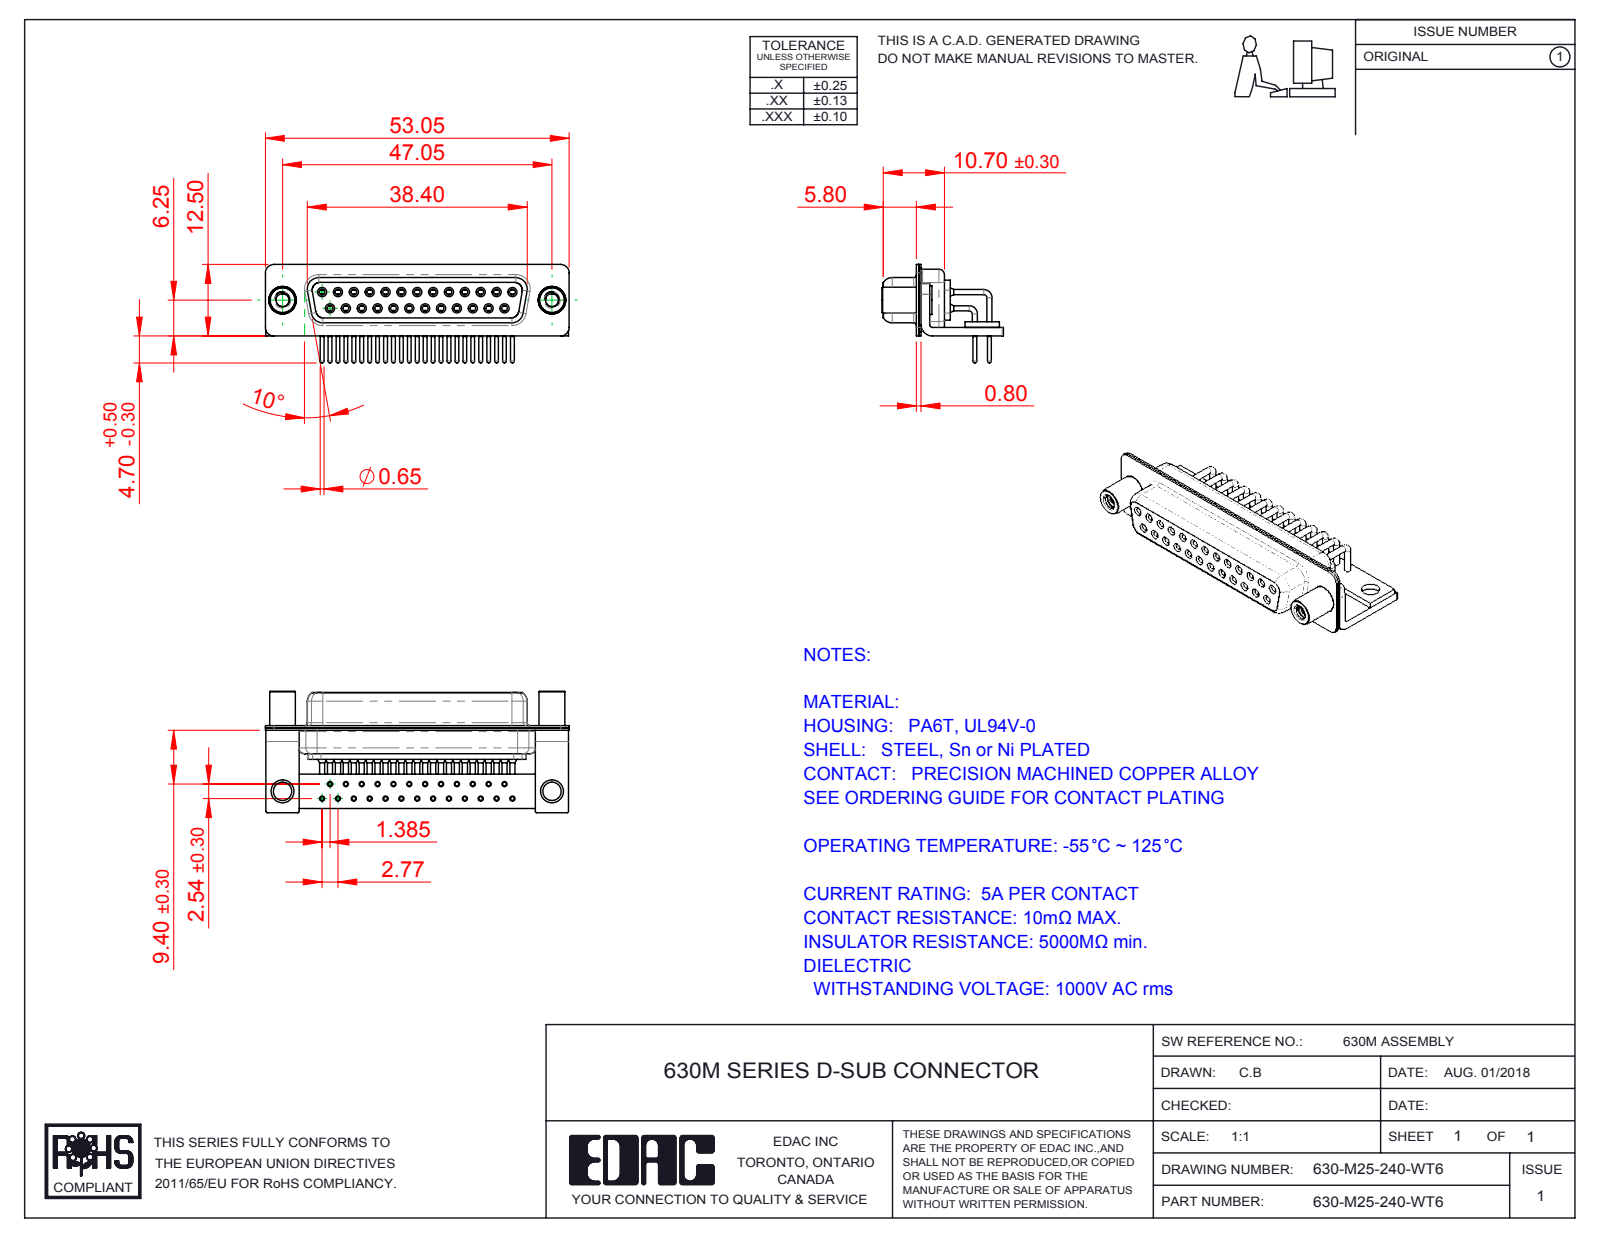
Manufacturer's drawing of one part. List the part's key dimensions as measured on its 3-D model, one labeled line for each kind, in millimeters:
Part name (STEP PRODUCT): 630-M25-240-WT6; 630M Housing_25 Contacts; 630M Shell Front_25 Contacts; 630M Shell Rear_25 Contacts (+5 more)
STEP written by: SolidWorks 2016 (CONFIG_CONTROL_DESIGN)
Units: millimetres
Bodies: 33 solids, 1754 faces (470 planar, 826 cylindrical, 458 other)
Overall size (bounding box): 53.05 × 21.2 × 17.2
Volume: 4 578 mm³ · Surface area: 11 419 mm²
Round holes (diameter × count): ⌀0.9 ×25, ⌀1 ×25, ⌀1.1 ×25, ⌀1.7 ×25, ⌀1.8 ×25, ⌀2 ×25, ⌀2.26 ×2, ⌀3.2 ×2, ⌀4 ×2, ⌀4.8 ×2
Round bosses / shafts (diameter × count): ⌀1.6 ×25, ⌀1.5 ×25, ⌀0.9 ×25, ⌀0.65 ×25, ⌀5 ×2, ⌀4.9 ×2, ⌀4.5 ×2
Partial cylindrical surfaces — rounded edges, fillets, slot ends (radius × count): R0.25 ×16, R1.5 ×16, R2 ×13, R1.35 ×10, R1.6 ×8, R0.5 ×5, R0.6 ×4, R0.65 ×4
Main face-to-face distances: 0.4, 2.3, 1.9, 1.45, 8.95, 0.85, 9.35, 0.8, 6.2, 1
Hole centre spacings: 2.77, 5.54, 8.31, 11.08, 13.85, 3.16, 4.87, 16.62
